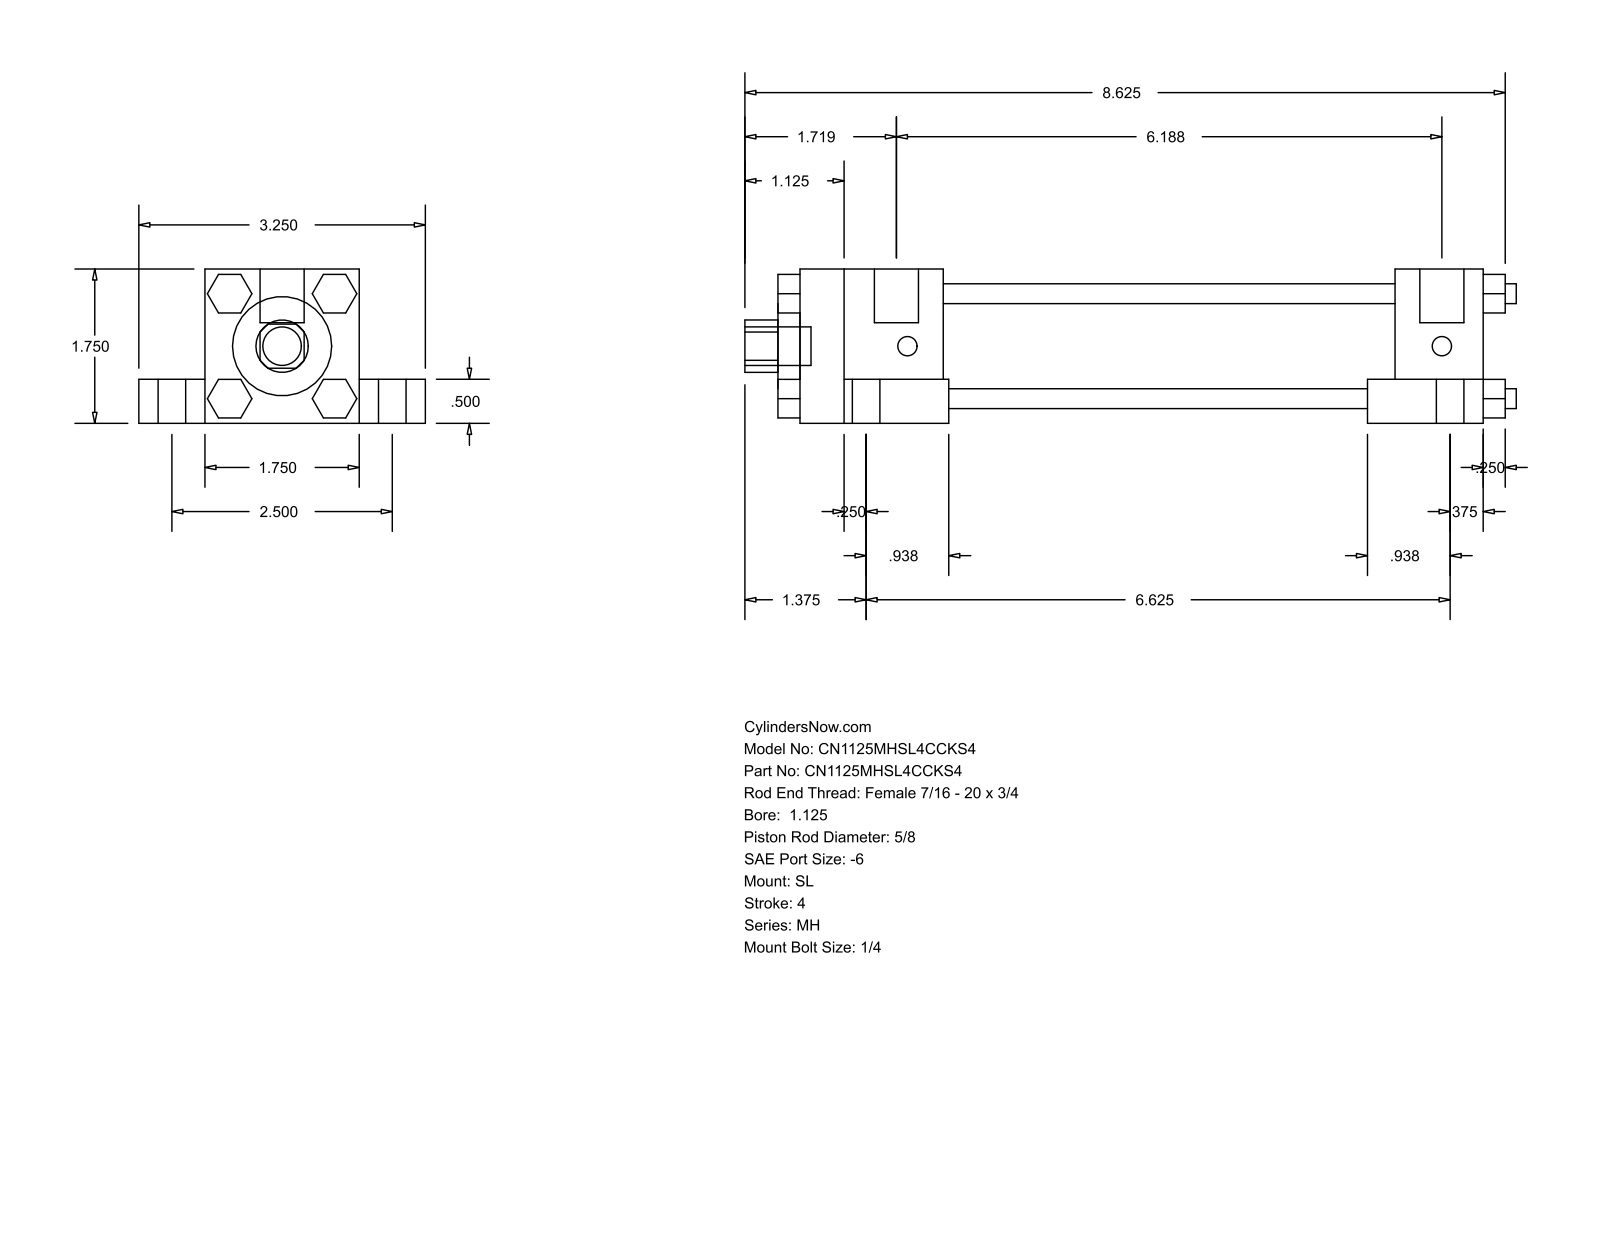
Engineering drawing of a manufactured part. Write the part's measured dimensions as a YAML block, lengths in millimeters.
part_name: "MH_SL__0112_0.625"
step_written_by: "GSSL Pune (CONFIG_CONTROL_DESIGN)"
units: millimeters
bodies: {solids: 0, faces: 150, planar: 114, cylindrical: 36, other: 0}
overall_size: [222.25, 82.55, 44.45]
round_holes:
  - {diameter: 15.88, count: 1}
  - {diameter: 28.57, count: 1}
  - {diameter: 34.92, count: 1}
round_bosses_or_shafts:
  - {diameter: 14.29, count: 4}
  - {diameter: 7.94, count: 4}
  - {diameter: 5.71, count: 4}
  - {diameter: 5.56, count: 4}
  - {diameter: 12.7, count: 2}
  - {diameter: 11.11, count: 1}
partial_cylinders:
  - {radius: 7.54, count: 1}
face_to_face_distances: [44.46, 19.04, 12.7, 31.76, 63.5, 6.35, 203.19, 11.11, 130.17, 155.57]
